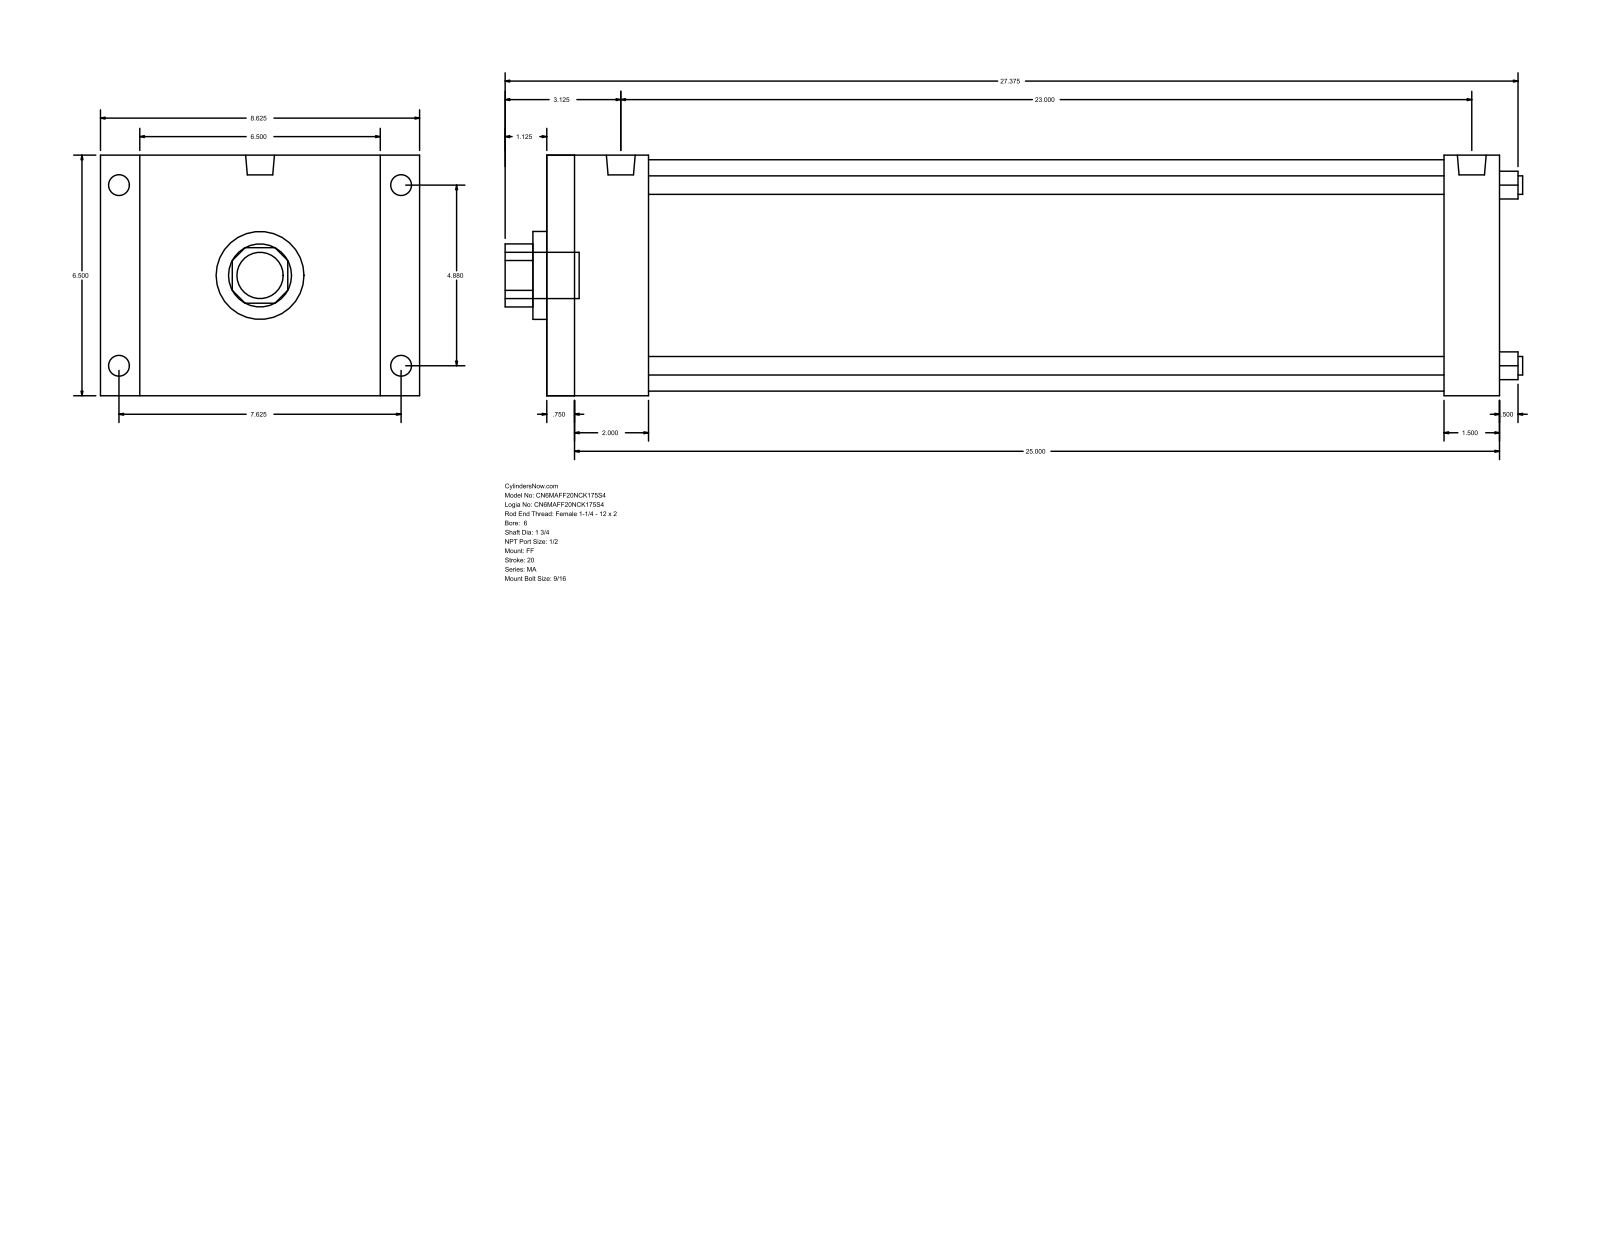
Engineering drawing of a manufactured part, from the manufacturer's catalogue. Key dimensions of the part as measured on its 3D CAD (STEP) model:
Part name (STEP PRODUCT): MA_FF__0600_1.75
STEP written by: GSSL Pune (CONFIG_CONTROL_DESIGN)
Units: millimetres
Bodies: 0 solids, 92 faces (64 planar, 28 cylindrical, 0 other)
Overall size (bounding box): 698.5 × 219.07 × 165.1
Round holes (diameter × count): ⌀12.7 ×4, ⌀44.45 ×1, ⌀60.33 ×1, ⌀158.75 ×1
Round bosses / shafts (diameter × count): ⌀17.46 ×4, ⌀14.29 ×4, ⌀19.77 ×2, ⌀31.75 ×1
Partial cylindrical surfaces — rounded edges, fillets, slot ends (radius × count): R21.63 ×1
Main face-to-face distances: 165.1, 654.05, 19.05, 635, 38.1, 50.8, 69.85, 584.2, 615.95, 596.9
Hole centre spacings: 87.65, 123.96, 175.31
